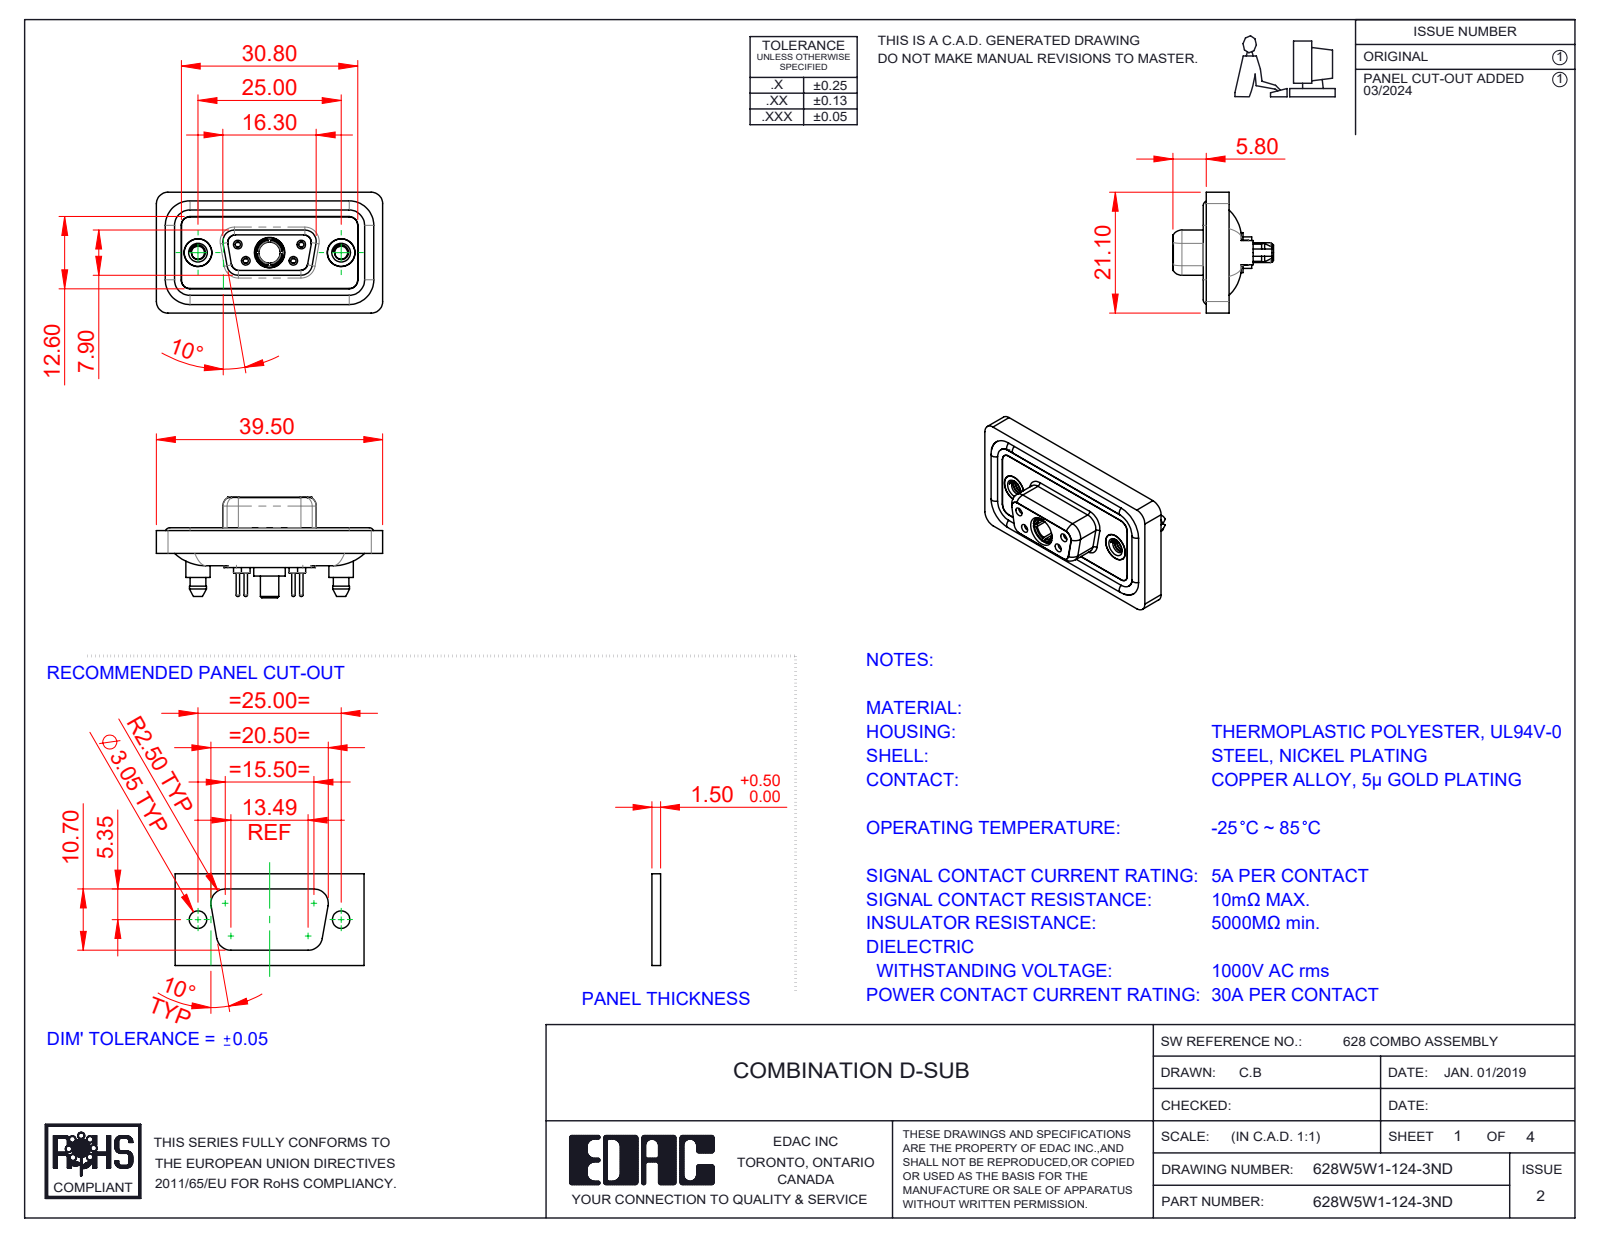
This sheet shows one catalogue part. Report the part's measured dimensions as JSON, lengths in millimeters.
{"part_name": "628Combo Contact Row 1_24; 628Combo Contact Row 2_24; 628Combo Waterproof Housing_09 Contacts; 628Combo Housing_5W1 (+5 more)", "step_written_by": "SolidWorks 2023 (CONFIG_CONTROL_DESIGN)", "units": "millimeters", "bodies": {"solids": 13, "faces": 746, "planar": 210, "cylindrical": 335, "other": 201}, "overall_size": [39.5, 21.1, 17.55], "volume_mm3": 4909, "surface_area_mm2": 7979, "round_holes": [[0.9, 4], [1.1, 4], [1.5, 4], [2, 4], [4.85, 3], [1.6, 2], [1.7, 2], [2.26, 2], [4, 2], [4.05, 2], [5, 2], [3.7, 1]], "round_bosses_or_shafts": [[1.6, 6], [2.2, 4], [0.6, 4], [5.4, 2], [4.95, 2], [4.8, 2], [4.25, 2], [5.5, 1]], "partial_cylinders_radius": [[1.5, 24], [2, 18], [1.6, 10], [1.35, 8], [0.25, 4], [0.5, 4], [0.6, 4], [0.65, 4]], "face_to_face_distances": [0.4, 2.9, 1.1, 1.8, 1.6, 0.5, 5.65, 7.45, 5.35, 3.6], "hole_center_spacings": [3.16, 5.72, 7.1, 12.5, 18.1, 4.39, 4.4, 8.31]}
